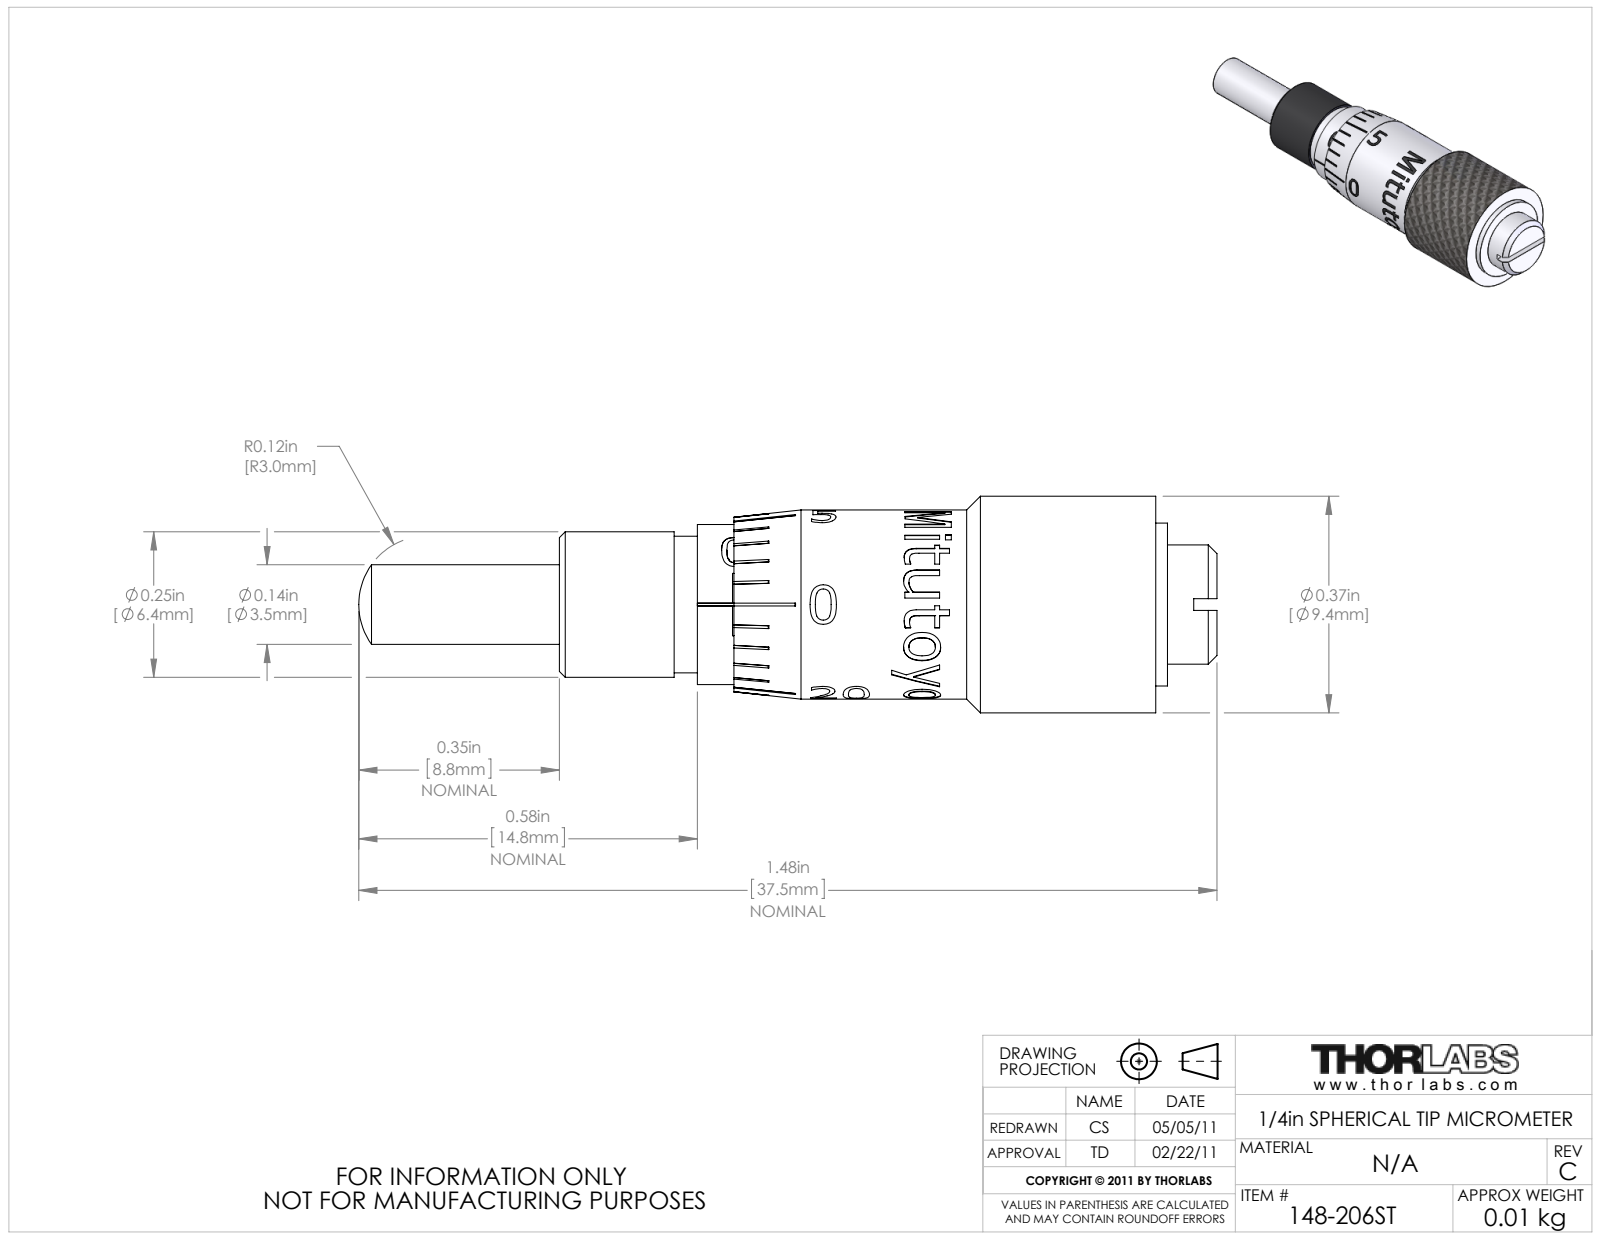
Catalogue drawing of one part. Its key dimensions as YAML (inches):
part_name: "13428-E0W"
step_written_by: "SolidWorks 2012 (AUTOMOTIVE_DESIGN)"
units: inches
bodies: {solids: 2, faces: 389, planar: 231, cylindrical: 53, other: 105}
overall_size: [1.475, 0.372, 0.372]
volume: 0.103
surface_area: 2.717
round_holes:
  - {diameter: 0.138, count: 1}
  - {diameter: 0.175, count: 1}
  - {diameter: 0.285, count: 1}
round_bosses_or_shafts:
  - {diameter: 0.372, count: 1}
  - {diameter: 0.325, count: 1}
  - {diameter: 0.28, count: 1}
  - {diameter: 0.275, count: 1}
  - {diameter: 0.255, count: 1}
  - {diameter: 0.25, count: 1}
  - {diameter: 0.235, count: 1}
  - {diameter: 0.205, count: 1}
partial_cylinders:
  - {radius: 0.137, count: 1}
  - {radius: 0.161, count: 1}
face_to_face_distances: [0.545, 0.02, 0.565, 1.045, 1.025, 0.48, 0.105, 0.085, 0.65, 1.13]
